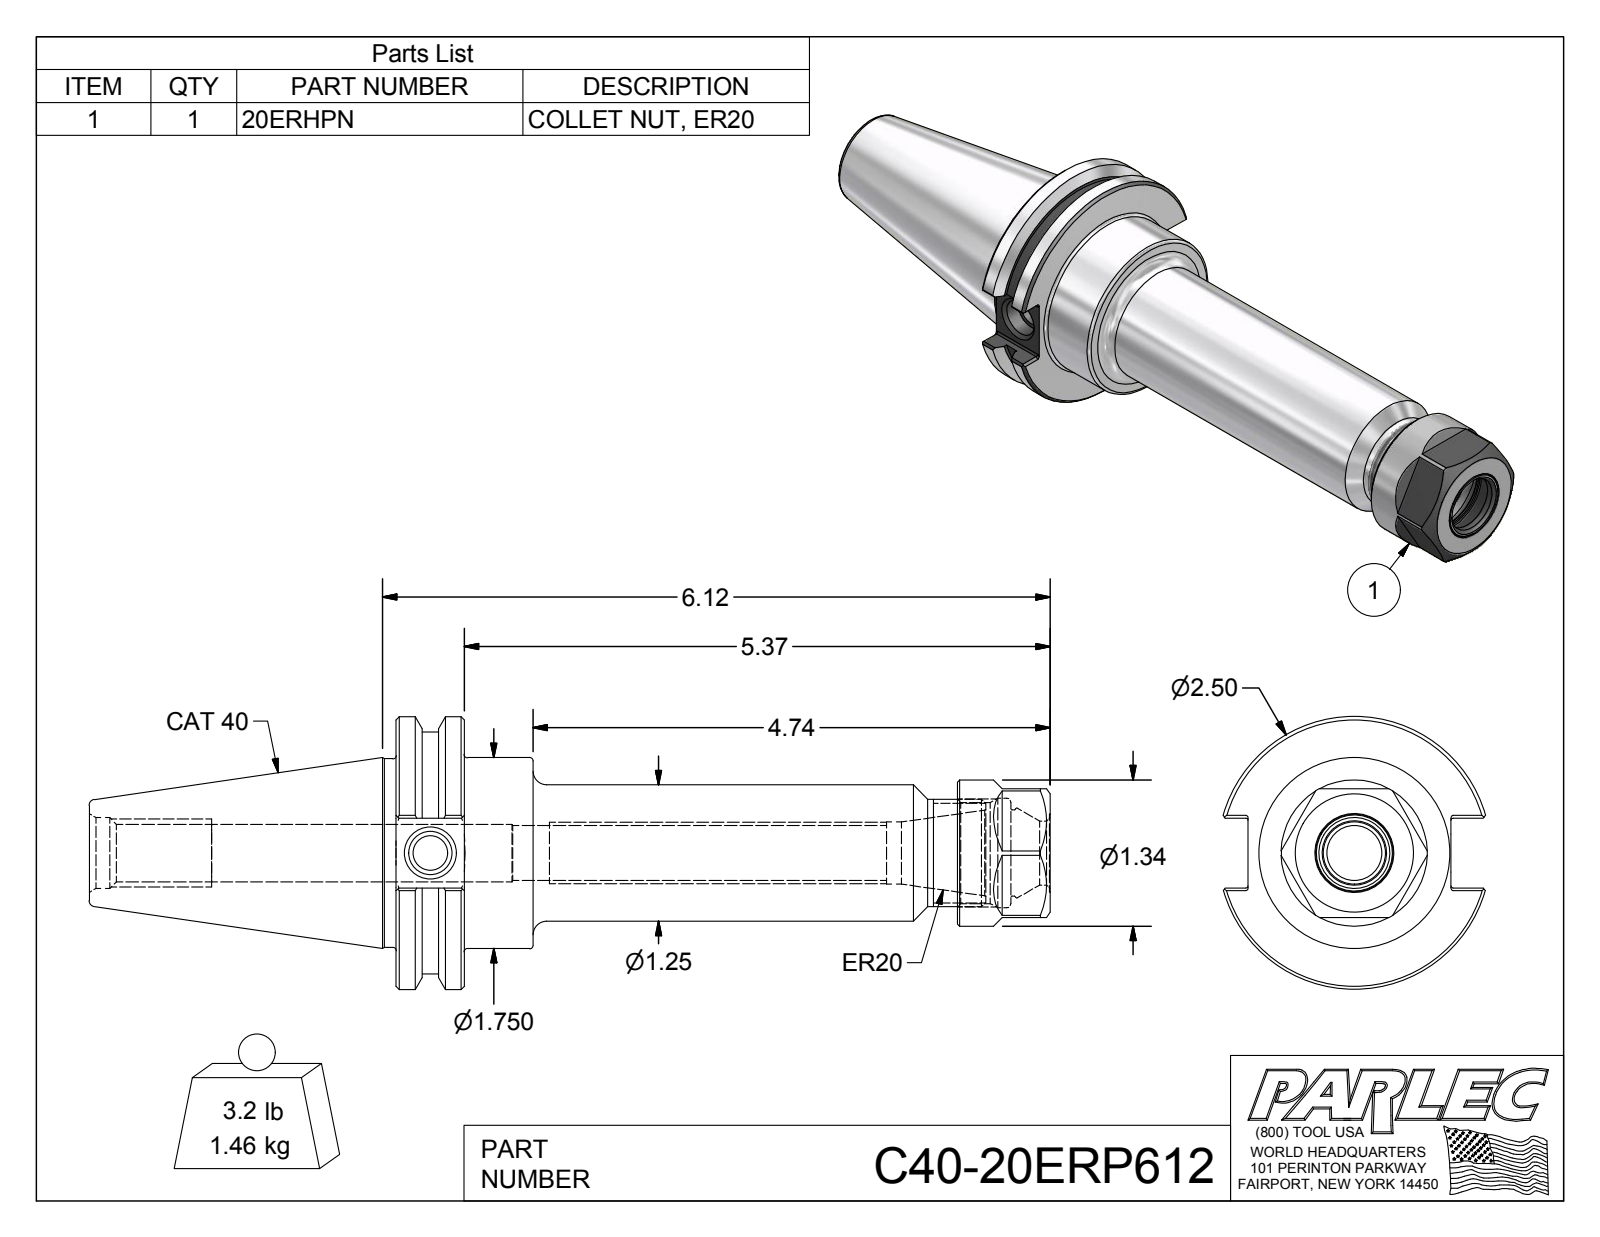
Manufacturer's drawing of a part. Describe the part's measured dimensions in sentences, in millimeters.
The part is named "C40-20ERP612; C40-20ER6-1; 20ERHPN". Its 3-D file was written by "Autodesk Inventor 2012 (AUTOMOTIVE_DESIGN)". It is 2 solids with 120 faces: 49 planar, 34 cylindrical and 37 other. Overall it measures 223.7 by 63.5 by 61 millimeters. Its volume is 196 300 cubic millimeters and its surface area 42 120 square millimeters. Round holes: 1 of diameter 8, 1 of diameter 10.1, 1 of diameter 12.8, 1 of diameter 13.4, 1 of diameter 13.4, 1 of diameter 14.5, 1 of diameter 14.9, 1 of diameter 16.5, 1 of diameter 20.1, 1 of diameter 23.5, 1 of diameter 25.5. Round bosses or shafts: 1 of diameter 63.5, 1 of diameter 56.4, 1 of diameter 44.5, 1 of diameter 43.9, 1 of diameter 34, 1 of diameter 31.8, 1 of diameter 25. Partial cylindrical surfaces (rounded edges, fillets, slot ends): 12 of radius 0.5. The main face-to-face distances are 15.9, 30, 130.7, 114.8, 152.3, 136.4, 21.6, 31.9, 16, 98.8.
